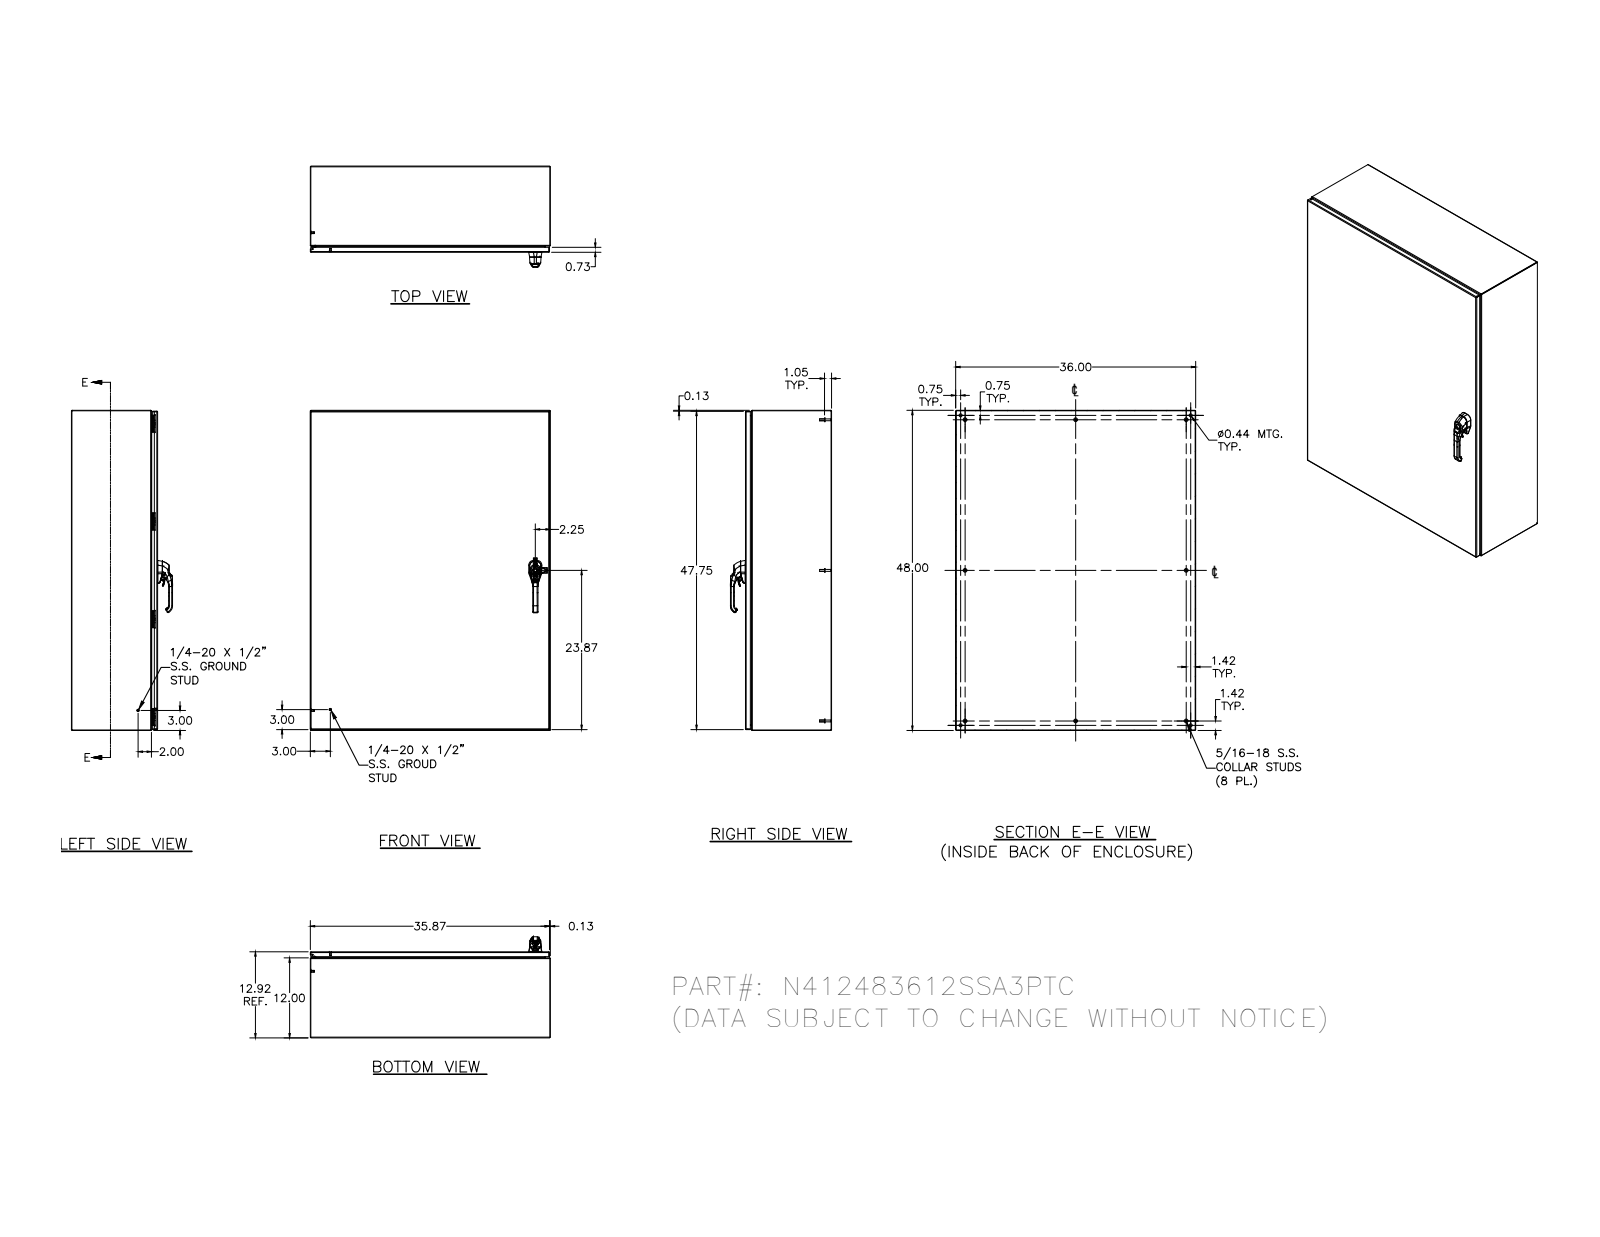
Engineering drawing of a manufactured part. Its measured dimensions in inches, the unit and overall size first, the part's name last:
Units: inches
Overall size (bounding box): 48 × 36 × 15.166
Round holes (diameter × count): ⌀0.093 ×8, ⌀0.152 ×8, ⌀0.167 ×8, ⌀0.172 ×8, ⌀0.187 ×8, ⌀0.165 ×5, ⌀0.156 ×4, ⌀0.197 ×4, ⌀0.437 ×4, ⌀0.213 ×3, ⌀0.106 ×2, ⌀0.16 ×2
Round bosses / shafts (diameter × count): ⌀0.25 ×18, ⌀0.563 ×8, ⌀0.36 ×8, ⌀0.32 ×8, ⌀0.3 ×8, ⌀0.275 ×8, ⌀0.256 ×8, ⌀0.164 ×8
Partial cylindrical surfaces — rounded edges, fillets, slot ends (radius × count): R0.02 ×188, R0.012 ×100, R0.05 ×50, R0.031 ×36, R0.016 ×34, R0.125 ×32, R0.019 ×23, R0.118 ×23
Main face-to-face distances: 0.074, 12.843, 12.769, 12.917, 35.926, 47.926, 35.852, 36, 47.852, 48
Hole centre spacings: 14.667, 29.333, 14.667, 44, 29.333, 0.5, 0.656, 14.675
Volume: 442 in³ · Surface area: 11 832 in²
Bodies: 87 solids, 3972 faces (1320 planar, 1471 cylindrical, 1181 other)
Part name (STEP PRODUCT): N412483612SSA3PTC; N412483612SSA3PTCBTB; N4124812SSA3PTCLS; N4124812SSA3PTCRS (+8 more)
STEP written by: Autodesk Inventor 2011 (AUTOMOTIVE_DESIGN)
